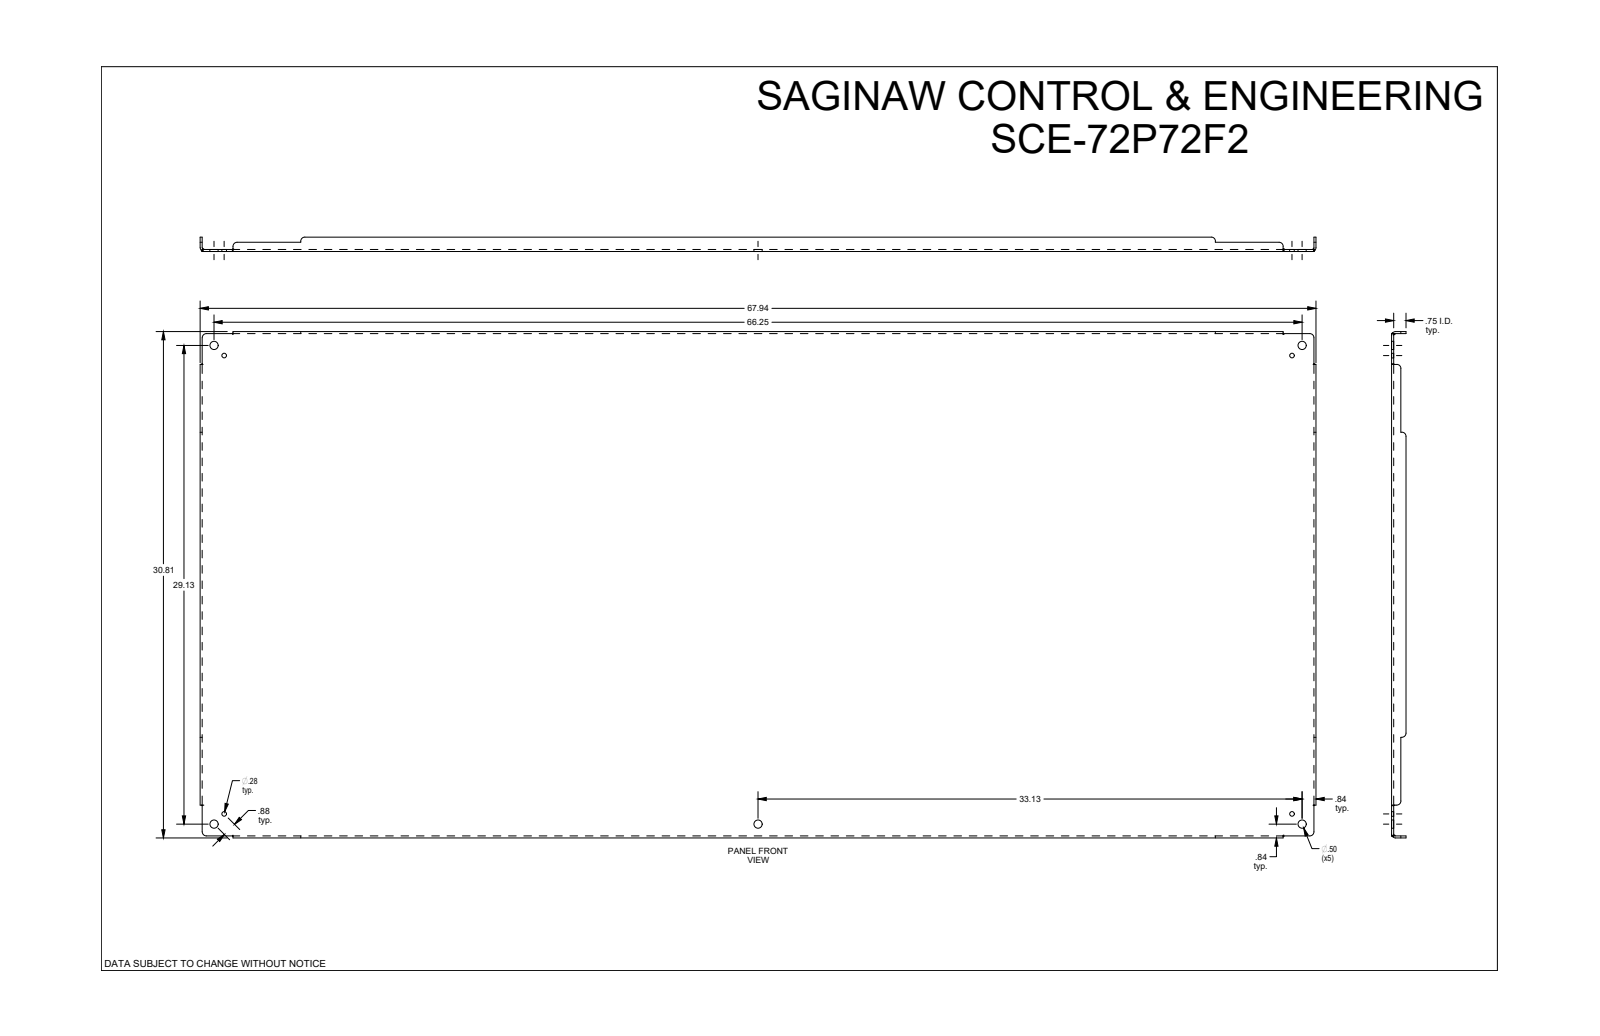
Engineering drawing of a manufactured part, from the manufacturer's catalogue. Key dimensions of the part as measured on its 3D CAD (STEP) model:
Part name (STEP PRODUCT): SCE-72P72F2
STEP written by: SolidWorks 2019 (CONFIG_CONTROL_DESIGN)
Units: inches
Bodies: 1 solid, 107 faces (46 planar, 37 cylindrical, 24 other)
Overall size (bounding box): 67.938 × 30.813 × 0.875
Volume: 275.3 in³ · Surface area: 4 431 in²
Round holes (diameter × count): ⌀0.5 ×5, ⌀0.281 ×4
Partial cylindrical surfaces — rounded edges, fillets, slot ends (radius × count): R0.25 ×12, R0.112 ×4, R0.237 ×4
Main face-to-face distances: 0.125, 0.125, 30.687, 30.562, 30.813, 67.813, 0.75, 0.875, 67.687, 67.938
Hole centre spacings: 0.875, 28.513, 65.634, 71.555, 27.887, 29.125, 32.512, 33.125
